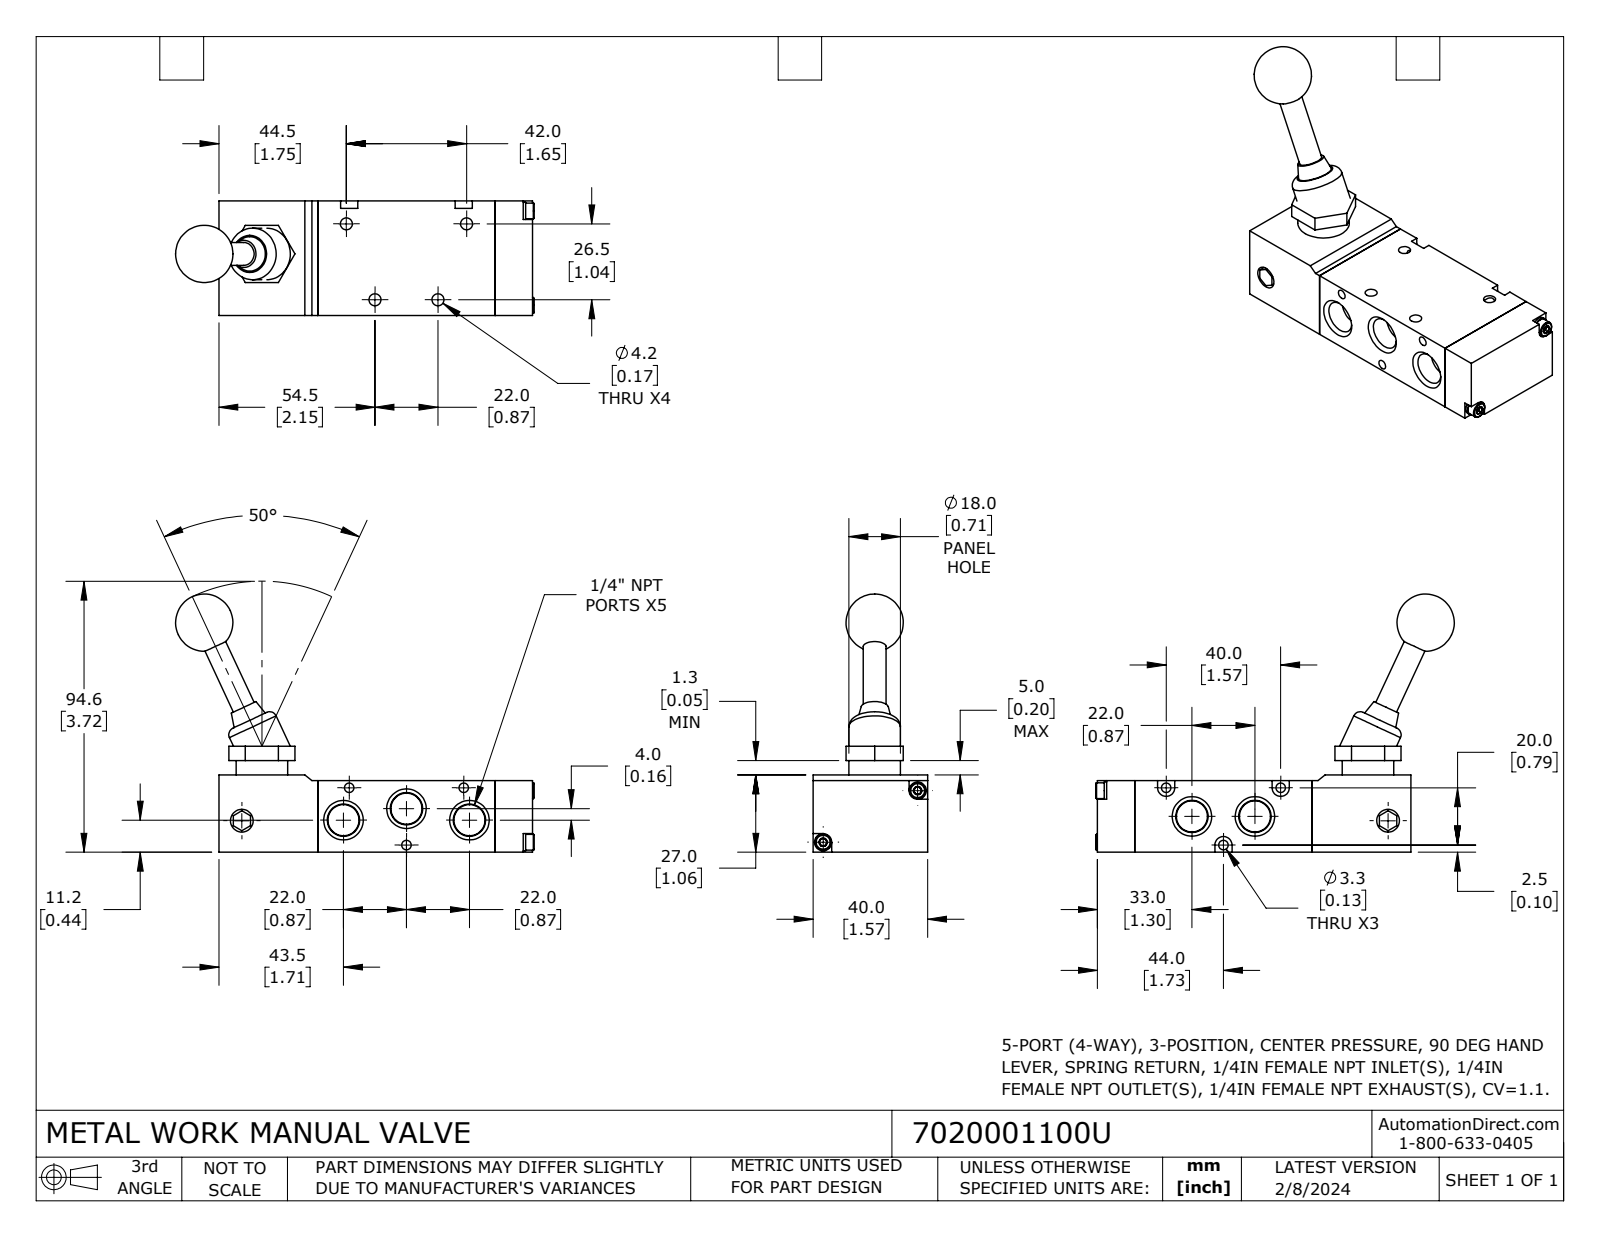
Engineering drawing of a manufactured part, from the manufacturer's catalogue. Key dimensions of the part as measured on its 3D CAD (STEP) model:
Part name (STEP PRODUCT): 7020001100U
STEP written by: SolidWorks 2023 (CONFIG_CONTROL_DESIGN)
Units: inches
Bodies: 8 solids, 206 faces (101 planar, 51 cylindrical, 54 other)
Overall size (bounding box): 4.93 × 3.549 × 1.575
Volume: 7.193 in³ · Surface area: 44.53 in²
Round holes (diameter × count): ⌀0.165 ×4, ⌀0.13 ×3, ⌀0.118 ×2, ⌀0.313 ×1
Round bosses / shafts (diameter × count): ⌀0.709 ×2, ⌀0.236 ×2, ⌀0.217 ×2, ⌀0.315 ×1
Partial cylindrical surfaces — rounded edges, fillets, slot ends (radius × count): R0.118 ×3
Main face-to-face distances: 0.984, 1.575, 2.441, 3.799, 1.358, 1.063, 0.079, 0.512, 2.953, 4.311
Hole centre spacings: 1.113, 1.115, 1.636, 0.866, 1.48, 1.544, 1.575, 1.654
